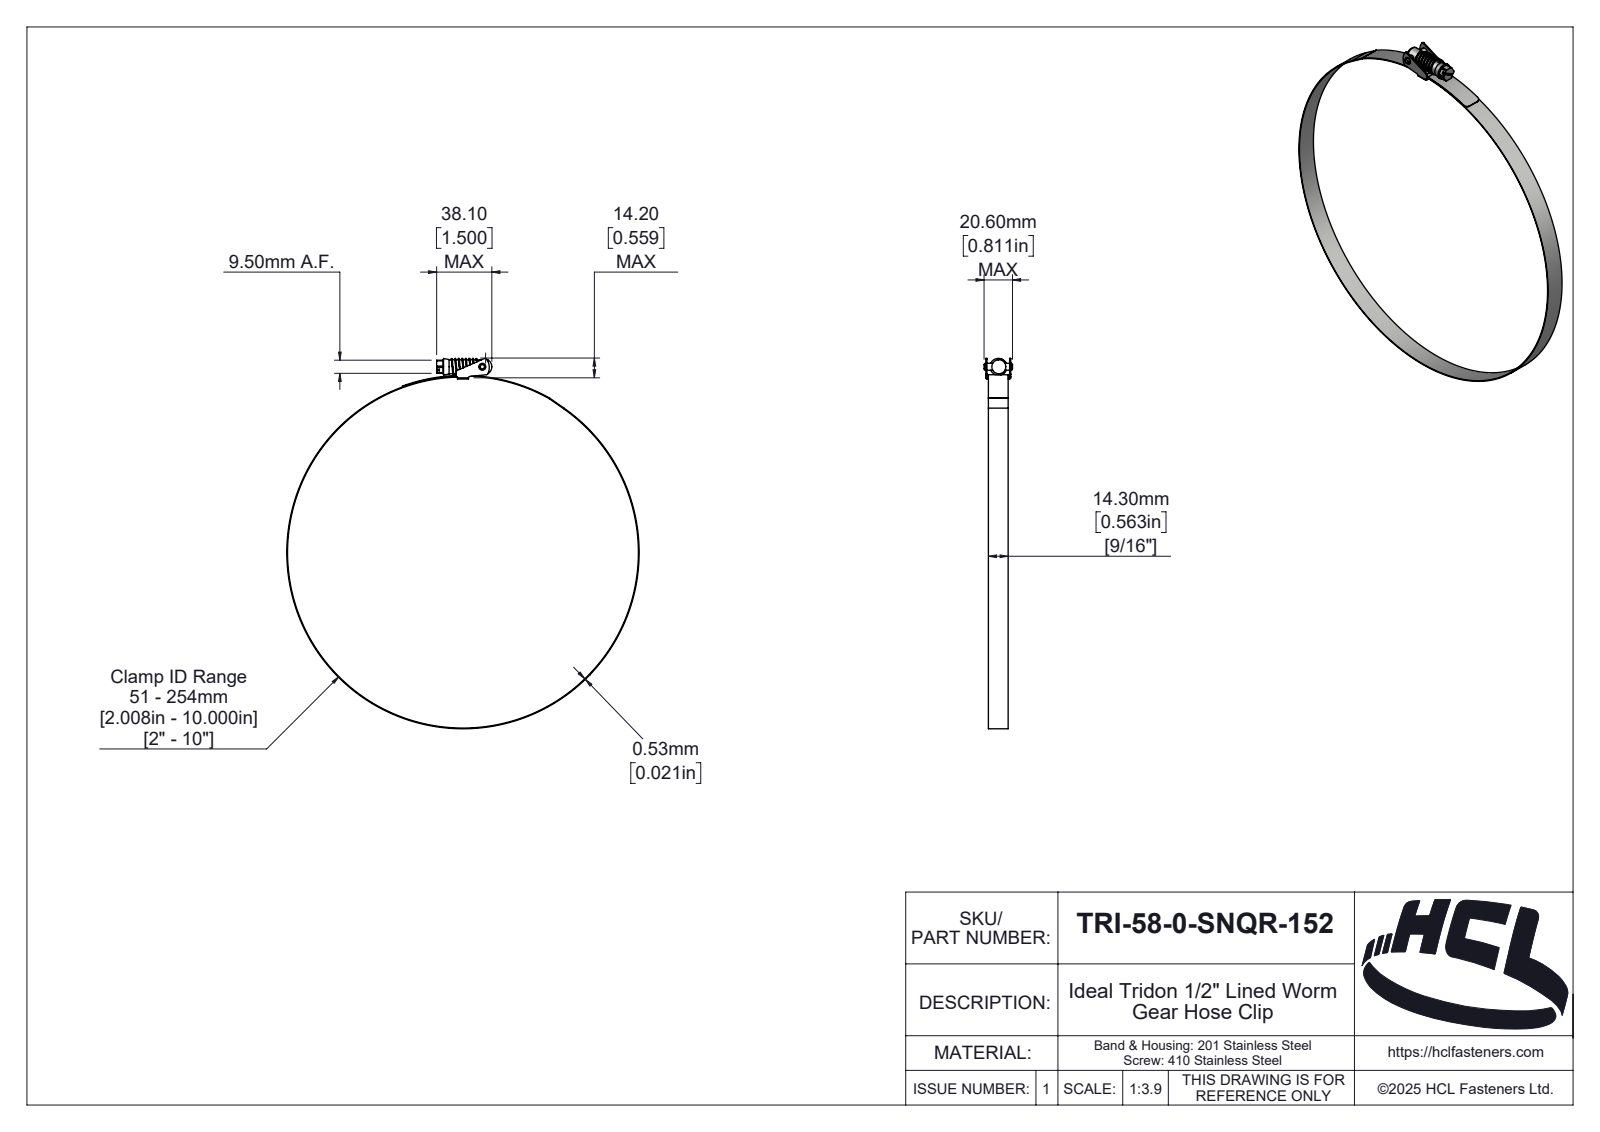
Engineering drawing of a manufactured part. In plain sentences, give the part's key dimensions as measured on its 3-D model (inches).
The part is named "TRI-58-0-SNQR-152". Its 3-D file was written by "SolidWorks 2025 (AUTOMOTIVE_DESIGN)". It is 5 solids with 222 faces: 44 planar, 112 cylindrical and 66 other. Overall it measures 10.552 by 10.042 by 0.811 inches. Its volume is 0.624 cubic inches and its surface area 44.95 square inches. Round holes: 1 of diameter 0.197, 1 of diameter 10. Round bosses or shafts: 1 of diameter 10.042, 1 of diameter 0.398. Partial cylindrical surfaces (rounded edges, fillets, slot ends): 11 of radius 0.039, 2 of radius 0.004, 2 of radius 0.035, 2 of radius 0.118, 1 of radius 0.018, 1 of radius 0.074, 1 of radius 0.079, 1 of radius 0.093. The main face-to-face distances are 0.031, 0.563, 0.677, 0.073, 0.636, 0.041, 0.604, 0.709, 0.646, 0.021. The hole center spacings are 5.32.
